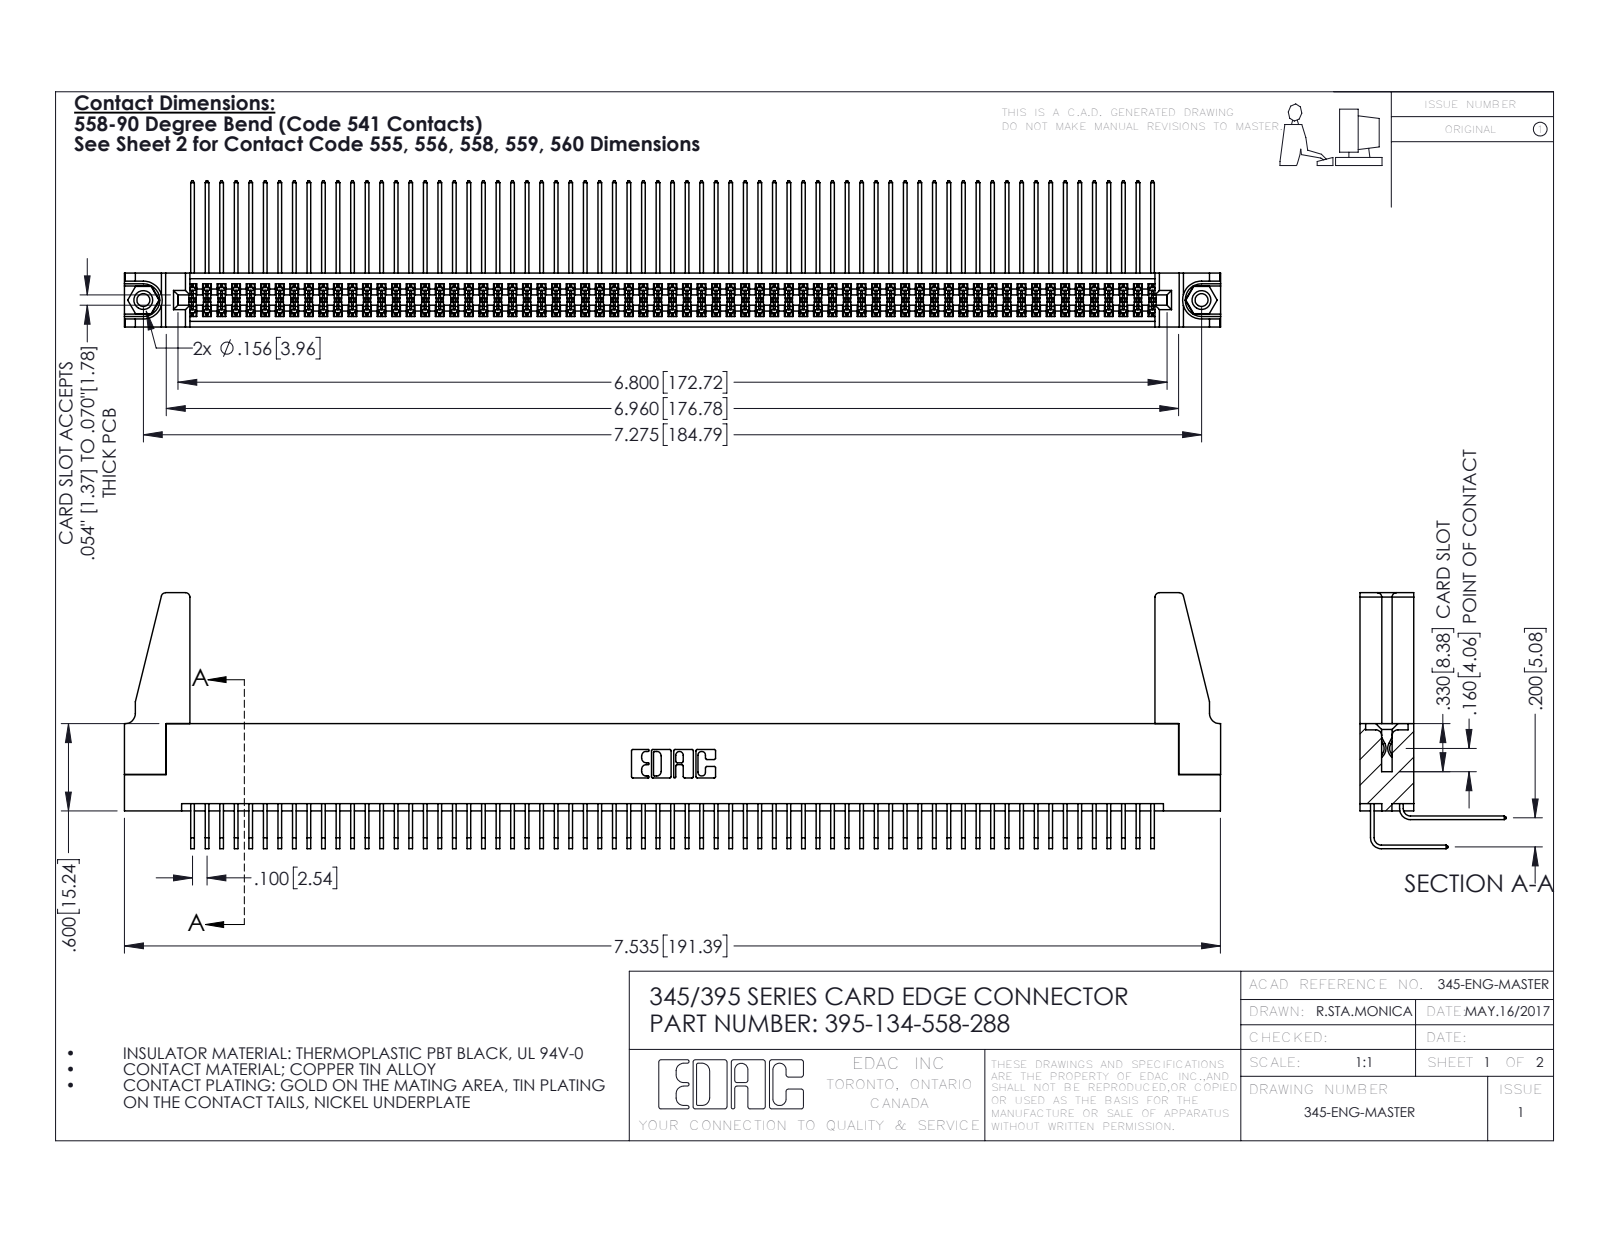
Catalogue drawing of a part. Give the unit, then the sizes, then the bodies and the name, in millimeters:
Units: millimetres
Overall size (bounding box): 191.4 × 44.7 × 25.5
Round holes (diameter × count): ⌀2.3 ×2, ⌀3.2 ×2, ⌀4 ×2, ⌀1.6 ×1
Round bosses / shafts (diameter × count): ⌀3.9 ×2
Partial cylindrical surfaces — rounded edges, fillets, slot ends (radius × count): R0.2 ×202, R0.3 ×22, R0.8 ×8, R0.2 ×6, R0.8 ×6, R0.7 ×3, R0.4 ×2, R0.5 ×2
Main face-to-face distances: 1.8, 7.6, 5.1, 9.4, 2.5, 6.9, 0.6, 5.7, 0.6, 4.4
Hole centre spacings: 6.9, 178.8, 184.8
Volume: 22 840 mm³ · Surface area: 36 210 mm²
Bodies: 139 solids, 7218 faces (4842 planar, 2360 cylindrical, 16 other)
Part name (STEP PRODUCT): 345-220-078_345-220-088; 395-134-558-288; 345-250-001_345-250-001-102; 345-292-001_558 559 Tail - 1 (+2 more)
STEP written by: SolidWorks 2016 (CONFIG_CONTROL_DESIGN)
